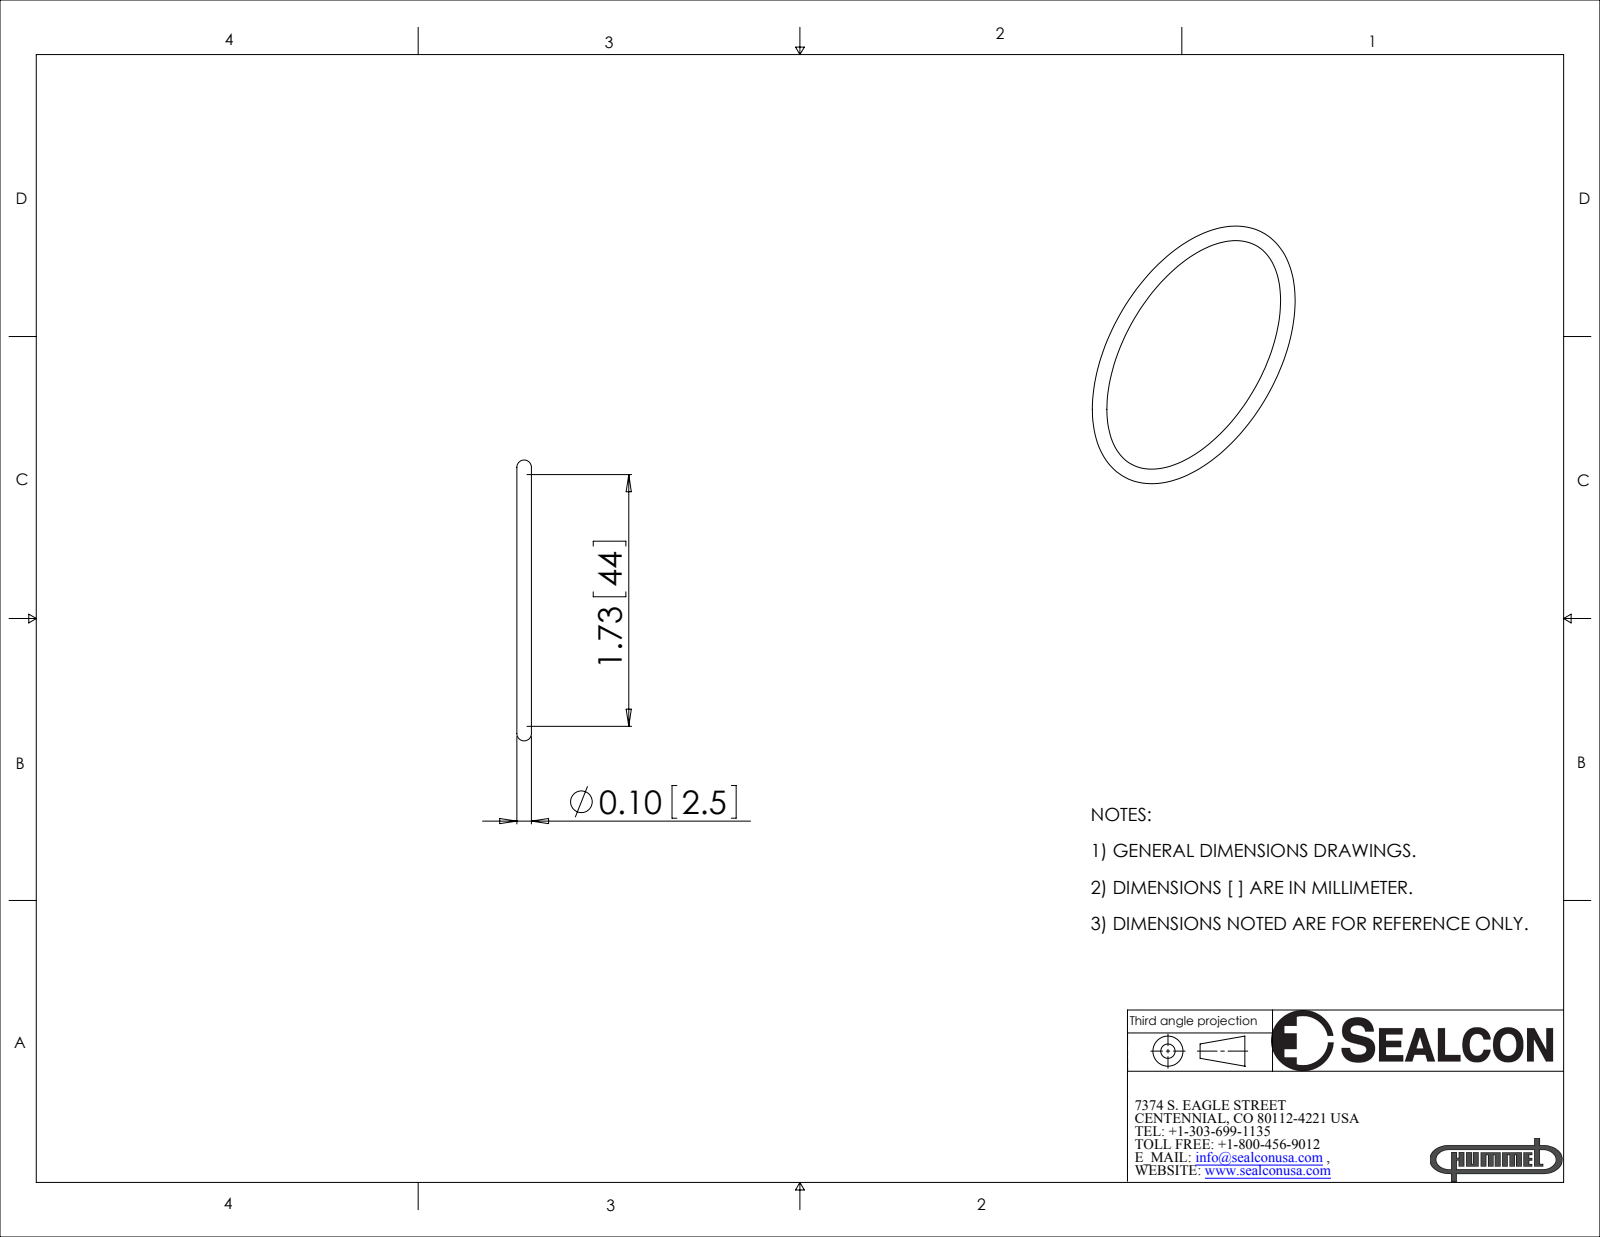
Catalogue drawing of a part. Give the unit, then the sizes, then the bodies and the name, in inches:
Units: inches
Overall size (bounding box): 1.93 × 1.93 × 0.1
Volume: 0.045 in³ · Surface area: 1.806 in²
Bodies: 1 solid, 4 faces (0 planar, 0 cylindrical, 4 other)
Part name (STEP PRODUCT): OR-36-SI
STEP written by: SolidWorks 2008 (CONFIG_CONTROL_DESIGN)
